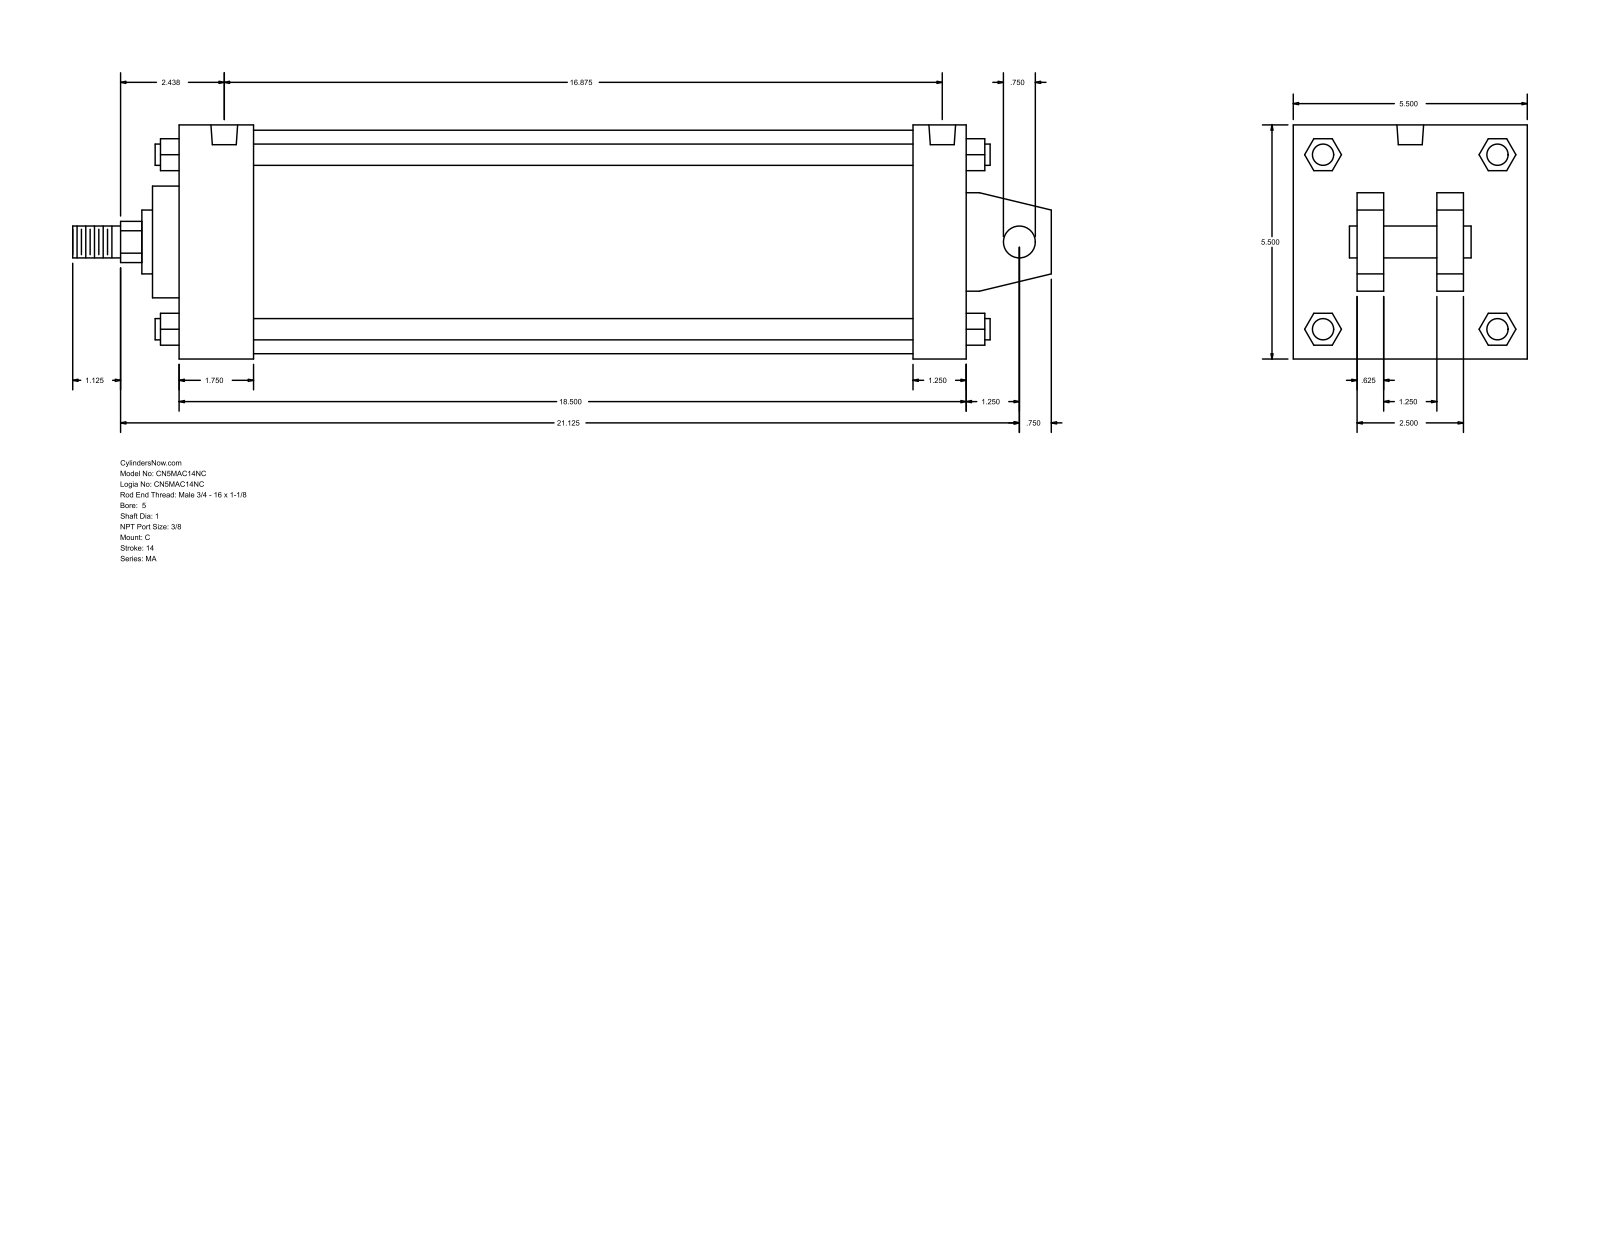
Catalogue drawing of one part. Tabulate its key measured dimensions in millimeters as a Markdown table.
| quantity | value |
| --- | --- |
| part name | MA_C__0500_1 |
| STEP written by | GSSL Pune (CONFIG_CONTROL_DESIGN) |
| units | millimeters |
| bodies | 0 solids, 141 faces (109 planar, 32 cylindrical, 0 other) |
| overall size | 584.2 × 139.7 × 139.7 |
| round holes (diameter × count) | 11.11 × 4, 15.93 × 2 |
| round bosses / shafts (diameter × count) | 12.7 × 4, 19.05 × 2, 133.35 × 1, 66.67 × 1, 38.1 × 1, 25.4 × 1 |
| partial cylindrical surfaces (radius × count) | 12.29 × 1 |
| main face-to-face distances | 139.7, 469.9, 15.87, 438.15, 31.75, 44.46, 393.69, 425.44, 38.1, 101.6 |
| hole center spacings | 419.1, 4.76, 4.77, 423.86, 423.87, 428.63 |
